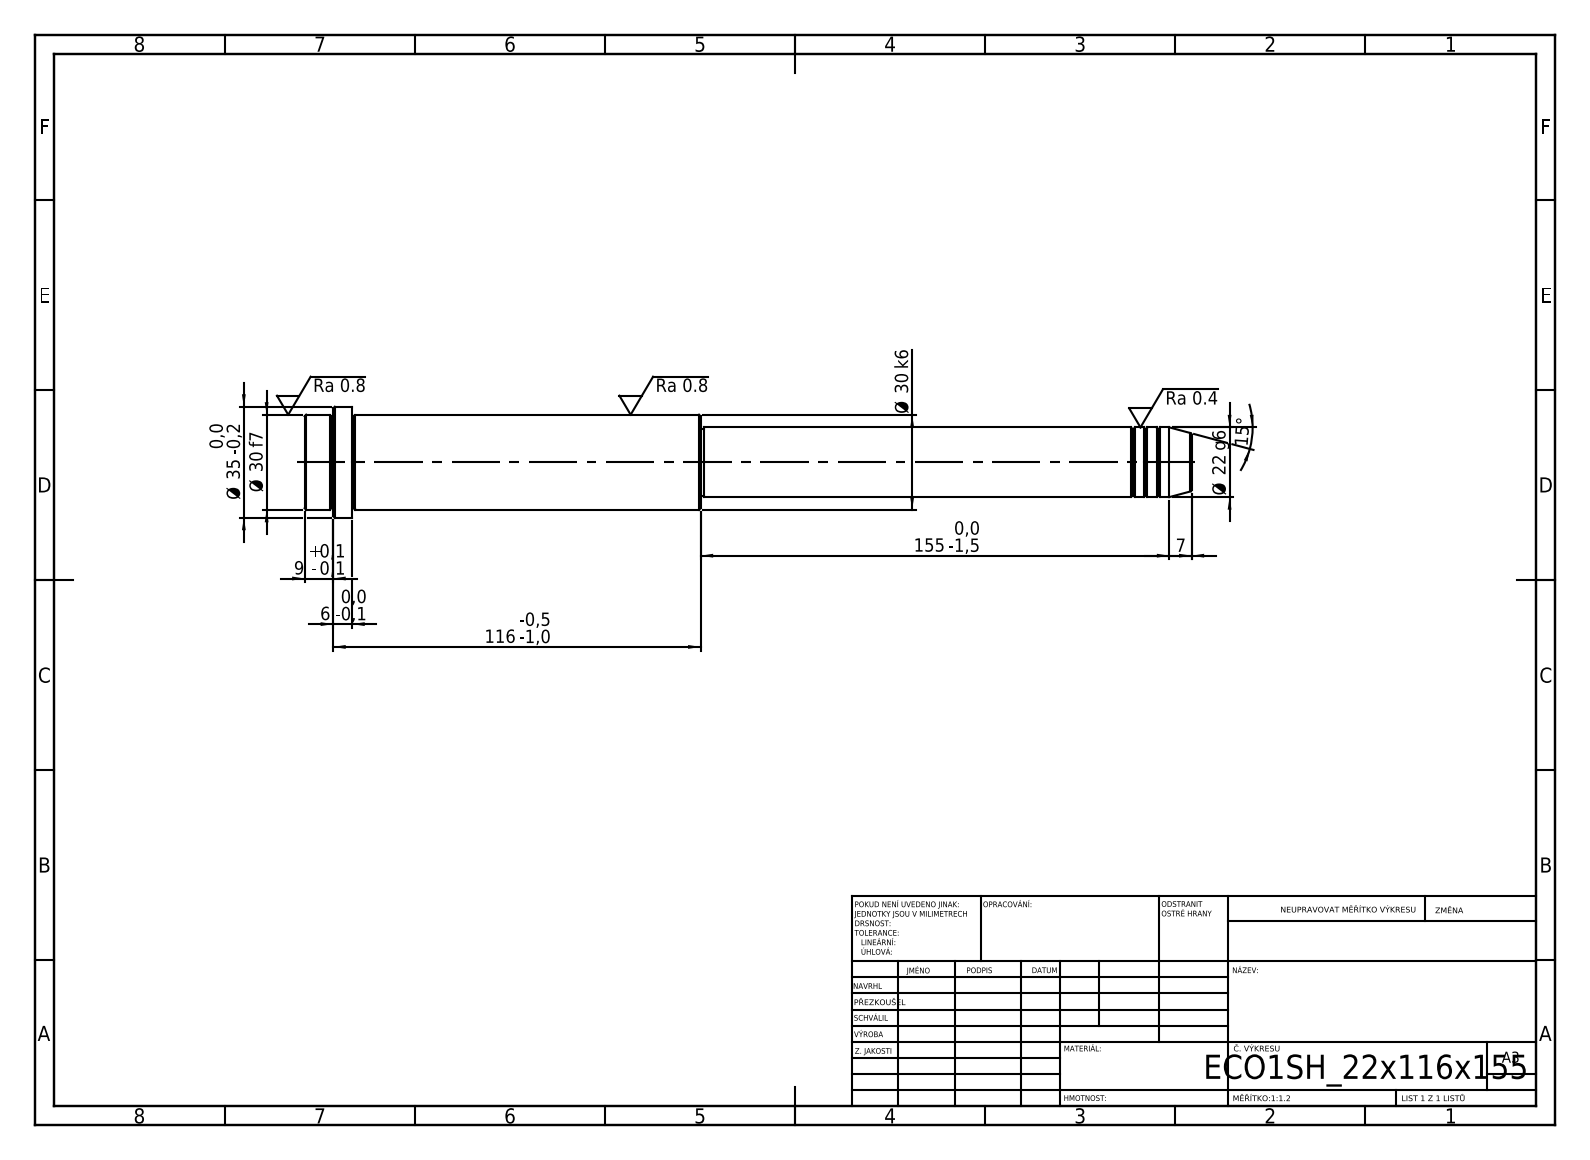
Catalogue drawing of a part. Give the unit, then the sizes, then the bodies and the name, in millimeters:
Units: millimetres
Overall size (bounding box): 280 × 35 × 35
Round bosses / shafts (diameter × count): ⌀35 ×1, ⌀30 ×1, ⌀22 ×1, ⌀21 ×1
Main face-to-face distances: 125, 110, 15, 155, 265, 280, 271, 116, 6, 9
Volume: 148 156 mm³ · Surface area: 24 548 mm²
Bodies: 1 solid, 52 faces (6 planar, 16 cylindrical, 30 other)
STEP written by: SolidWorks 2019 (CONFIG_CONTROL_DESIGN)
